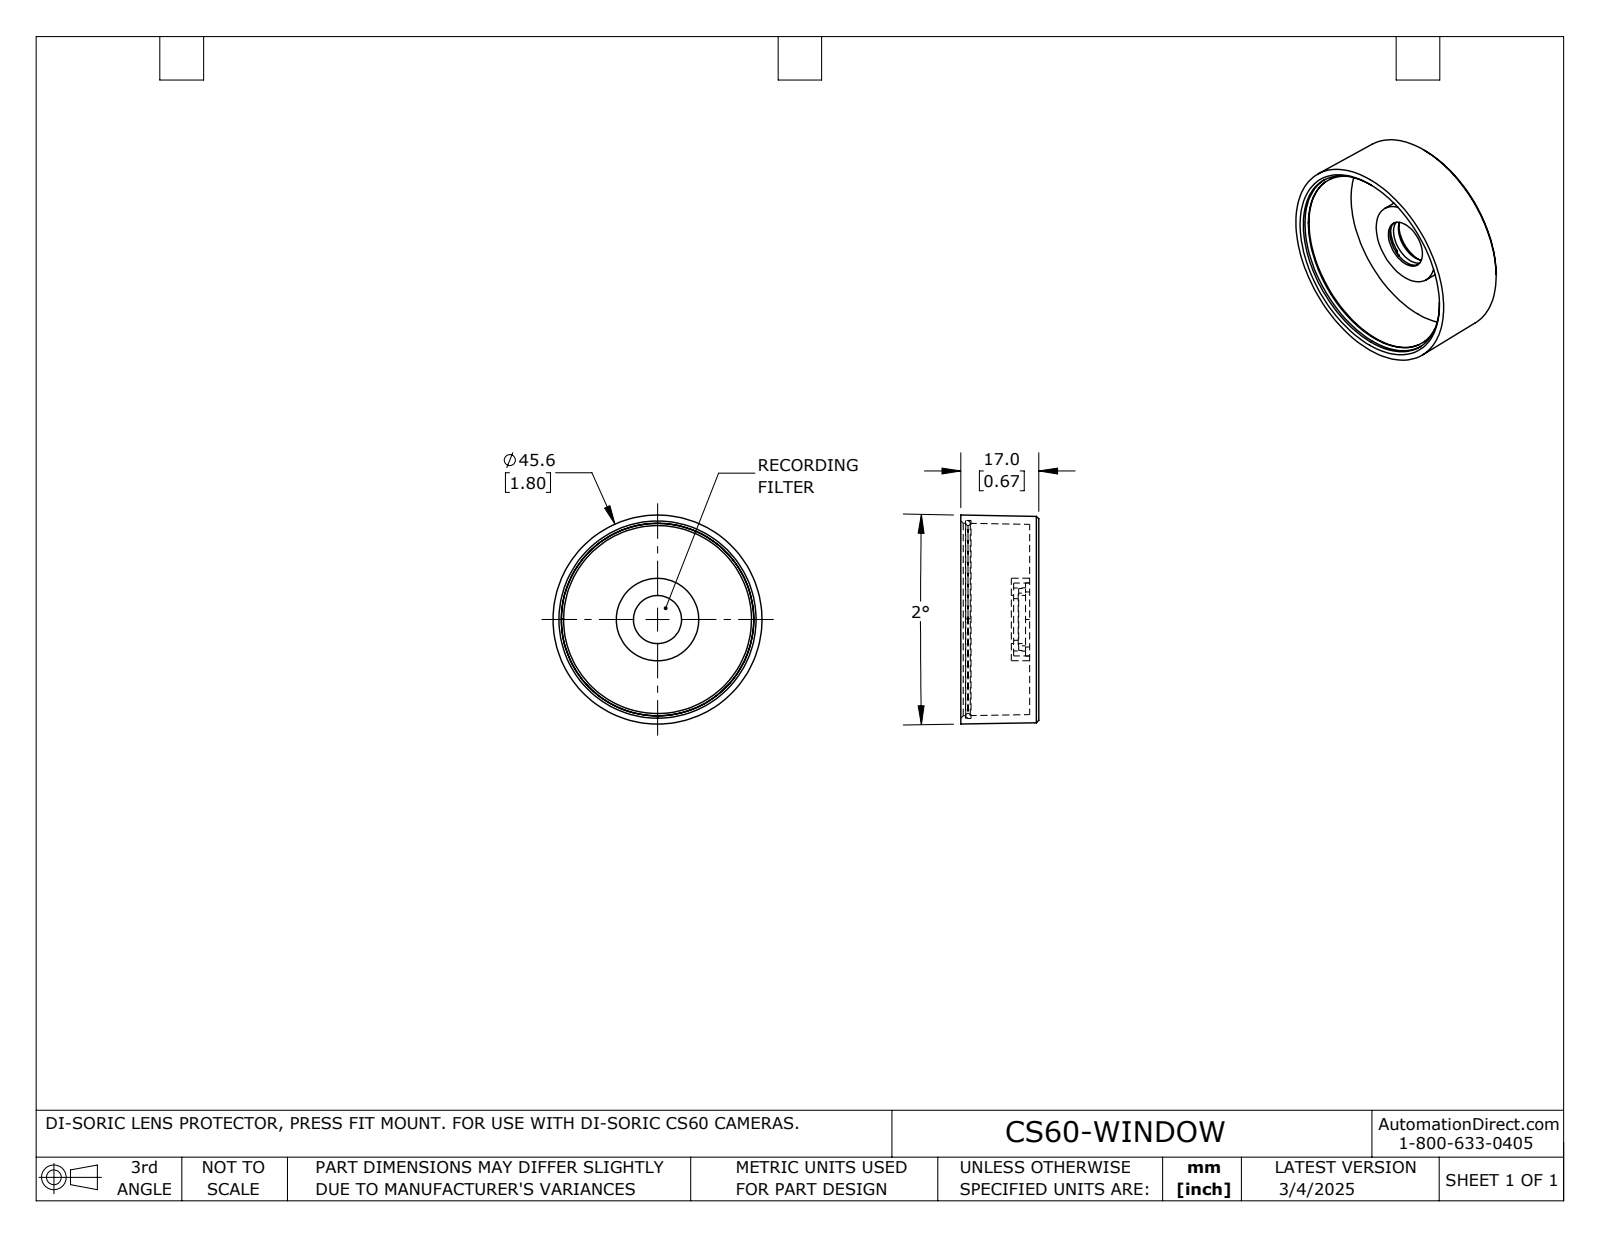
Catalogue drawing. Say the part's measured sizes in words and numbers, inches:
The part is named "CS60-WINDOW". Its 3-D file was written by "SolidWorks 2024 (AUTOMOTIVE_DESIGN)". It is 4 solids with 38 faces: 20 planar, 8 cylindrical and 10 other. Overall it measures 1.795 by 1.795 by 0.669 inches. Its volume is 0.449 cubic inches and its surface area 14.49 square inches. Round holes: 1 of diameter 0.413, 1 of diameter 0.626, 1 of diameter 1.701. Round bosses or shafts: 1 of diameter 0.709, 1 of diameter 0.531. Partial cylindrical surfaces (rounded edges, fillets, slot ends): 1 of radius 0.276. The main face-to-face distances are 0.079, 0.453, 0.591, 0.669, 0.433, 0.157, 0.236, 0.02, 0.138, 0.217.
